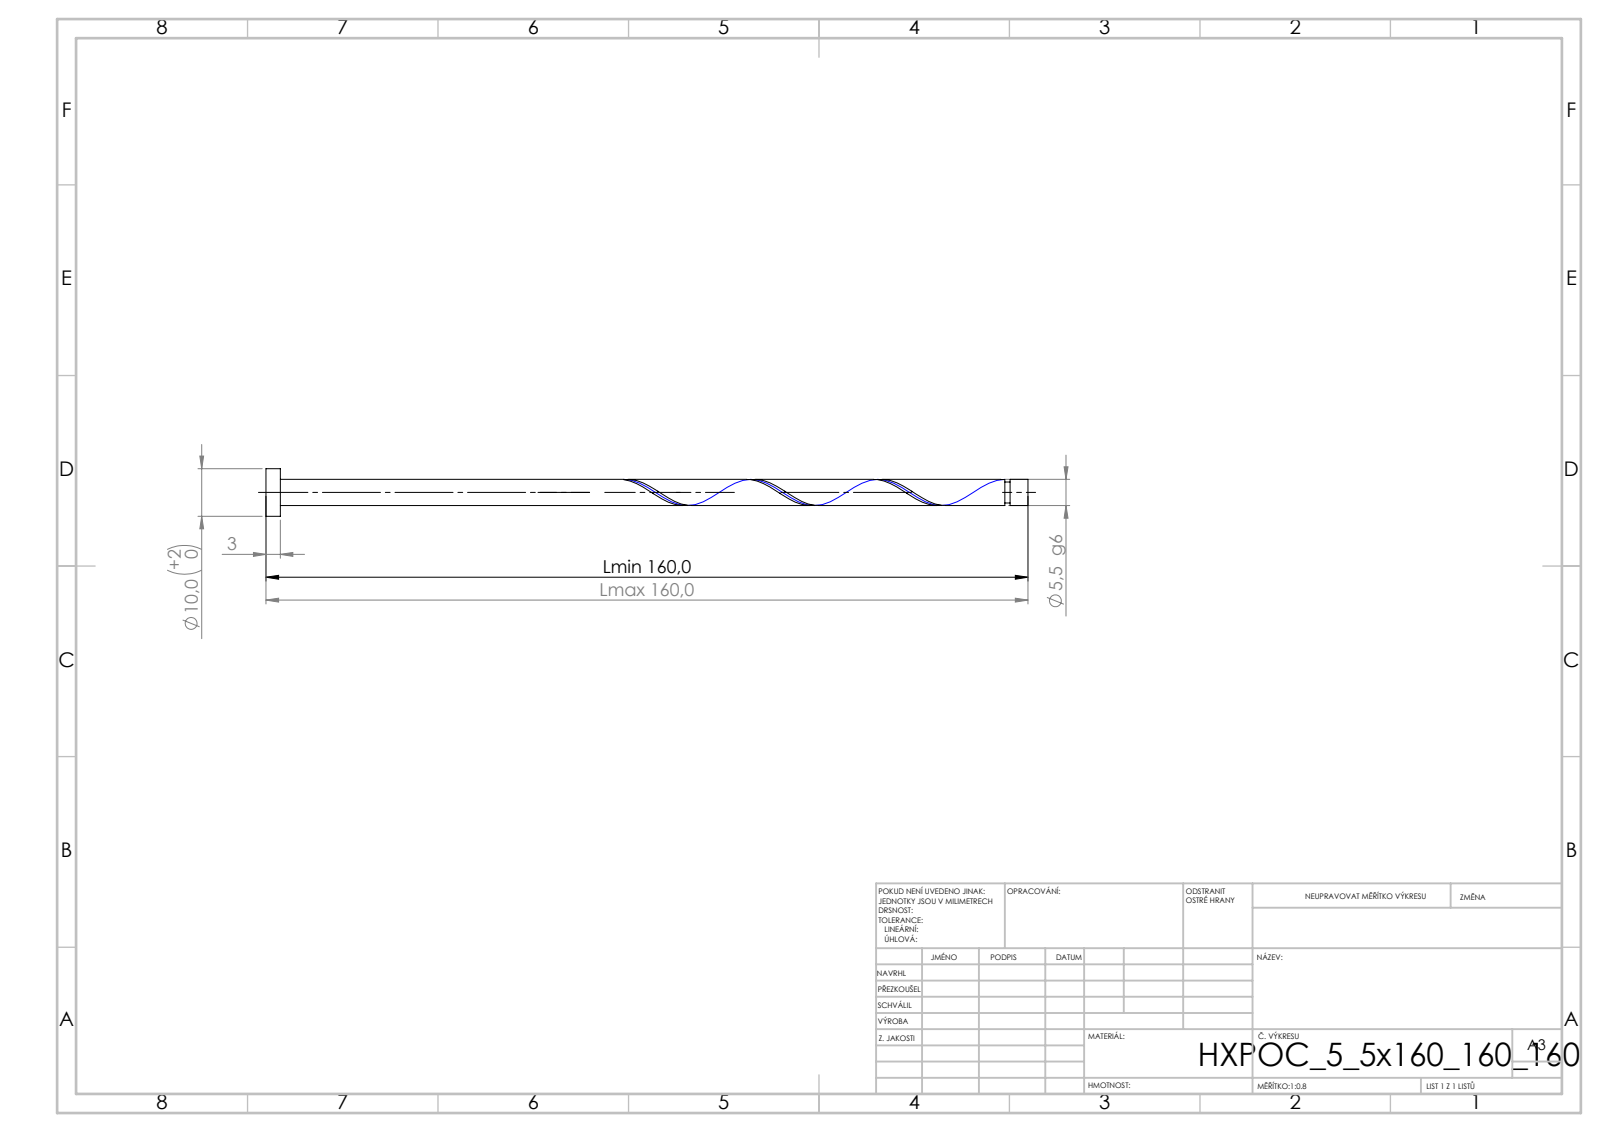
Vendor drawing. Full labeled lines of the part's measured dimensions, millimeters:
STEP written by: SolidWorks 2019 (CONFIG_CONTROL_DESIGN)
Units: millimetres
Bodies: 1 solid, 21 faces (6 planar, 14 cylindrical, 1 other)
Overall size (bounding box): 160 × 10 × 10
Volume: 3 920 mm³ · Surface area: 3 031 mm²
Round bosses / shafts (diameter × count): ⌀10 ×1, ⌀5.5 ×1, ⌀4.4 ×1
Main face-to-face distances: 3, 160, 157, 156.25, 153.25, 3.75, 155.15, 152.15, 1.1, 4.85
